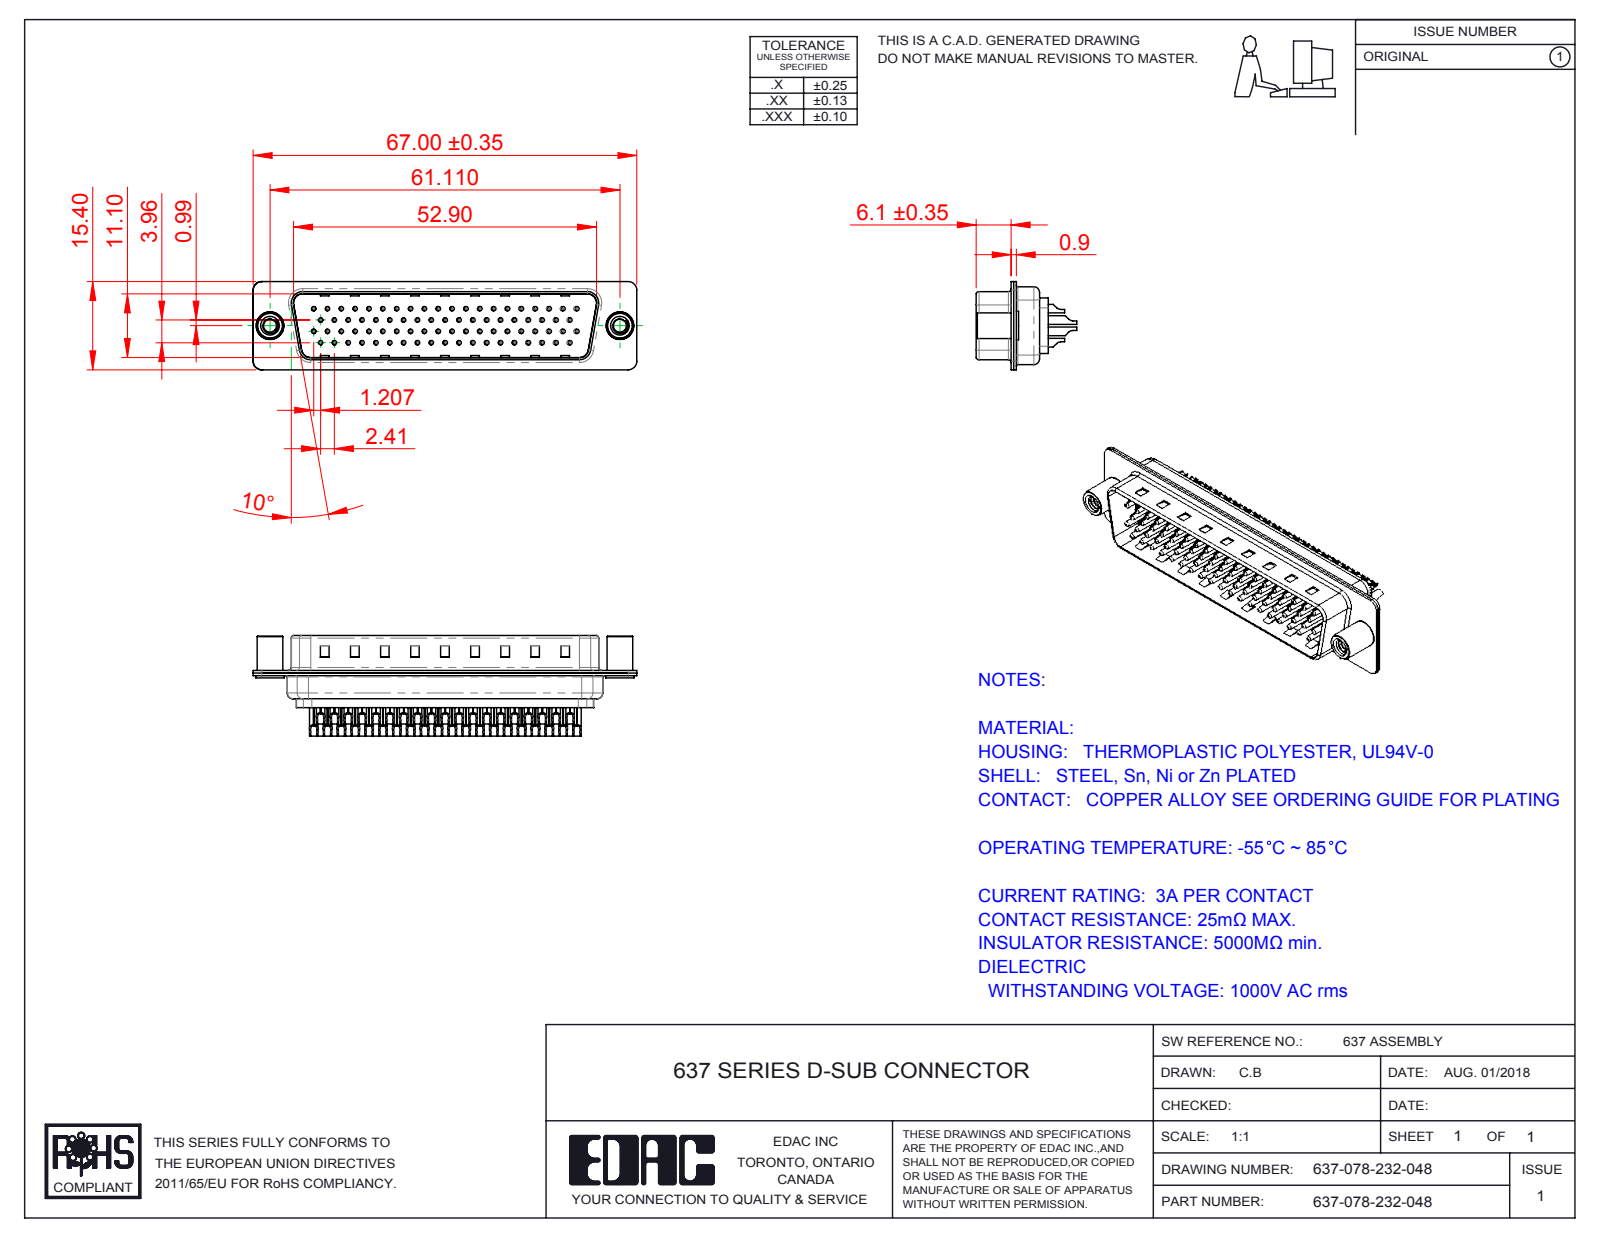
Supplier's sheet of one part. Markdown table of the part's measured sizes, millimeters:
| quantity | value |
| --- | --- |
| part name | 637 Contact Row 2_32(78); 637 4-40 Threaded Standoff; 637 Contact Row 78_32; 637 Shell Rear_78 Contacts (+5 more) |
| STEP written by | SolidWorks 2016 (CONFIG_CONTROL_DESIGN) |
| units | millimeters |
| bodies | 83 solids, 5438 faces (1297 planar, 2431 cylindrical, 1710 other) |
| overall size | 67 × 17.55 × 15.4 |
| volume | 4 497 mm³ |
| surface area | 16 973 mm² |
| round holes (diameter × count) | 1.6 × 150, 0.35 × 78, 1.1 × 78, 0.75 × 72, 2 × 72, 4 × 3, 2.26 × 2, 4.8 × 2 |
| round bosses / shafts (diameter × count) | 2 × 78, 1.5 × 78, 0.75 × 78, 5 × 2, 4.9 × 2, 4.5 × 2, 4.8 × 1 |
| partial cylindrical surfaces (radius × count) | 1.5 × 16, 2 × 12, 0.5 × 8, 1 × 8, 0.25 × 4, 0.55 × 4, 0.7 × 4, 0.95 × 4 |
| main face-to-face distances | 0.45, 0.4, 1.5, 1.95, 11.9, 11.5, 0.7, 11.1, 0.9, 0.8 |
| hole center spacings | 2.41, 7.24, 6.06, 9.65, 6.96, 8.46, 14.54, 16.89 |
